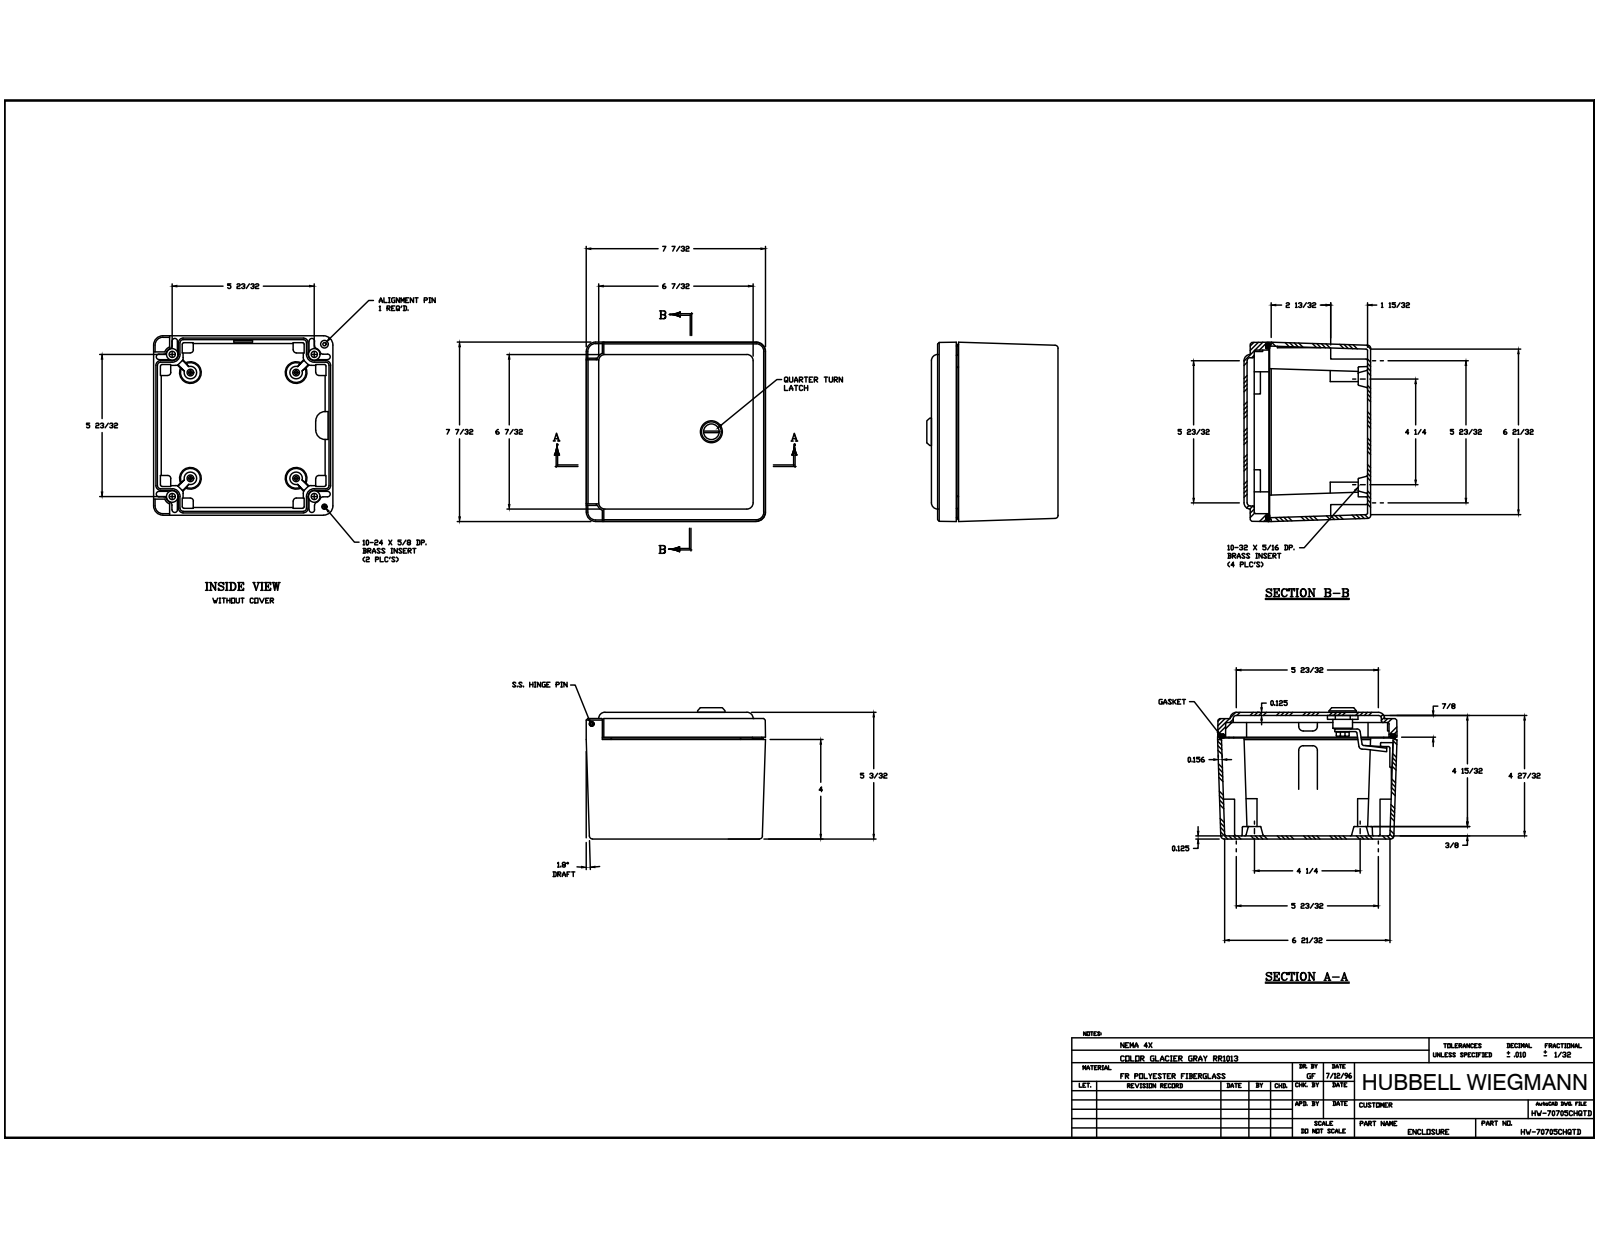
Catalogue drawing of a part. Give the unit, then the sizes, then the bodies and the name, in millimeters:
Units: millimetres
Overall size (bounding box): 183.4 × 183.39 × 134.14
Round holes (diameter × count): ⌀7.14 ×6, ⌀3.96 ×4, ⌀7.94 ×4, ⌀13.49 ×4, ⌀2.44 ×2, ⌀2.49 ×2, ⌀2.64 ×2, ⌀3.3 ×2, ⌀3.56 ×2, ⌀3.68 ×2, ⌀3.97 ×2, ⌀4.55 ×2
Round bosses / shafts (diameter × count): ⌀9.52 ×2, ⌀9.42 ×2, ⌀5.94 ×2, ⌀4.52 ×2, ⌀2.42 ×2, ⌀2.24 ×2, ⌀27.78 ×1, ⌀16 ×1
Partial cylindrical surfaces — rounded edges, fillets, slot ends (radius × count): R0.79 ×52, R1.59 ×31, R3.17 ×30, R7.94 ×11, R1.5 ×8, R9.53 ×8, R4.76 ×6, R3.97 ×5
Main face-to-face distances: 3.17, 4.72, 126.21, 129.38, 123.04, 3.18, 6.35, 19.05, 123.03, 119.86
Hole centre spacings: 128.01, 26.39, 107.98, 139.98, 145.3, 155.95, 179.1, 19.05
Volume: 830 557 mm³ · Surface area: 364 997 mm²
Bodies: 28 solids, 1073 faces (436 planar, 297 cylindrical, 340 other)
Part name (STEP PRODUCT): WP707HLBOX; 0.3125-18 X 0.563 DP BRASS INSERT; 10-32 X0.3125 DP BRASS INSERT; 10-24 X 0.625 DP BRASS INSERT (+8 more)
STEP written by: Autodesk Inventor 2014 (AUTOMOTIVE_DESIGN)
